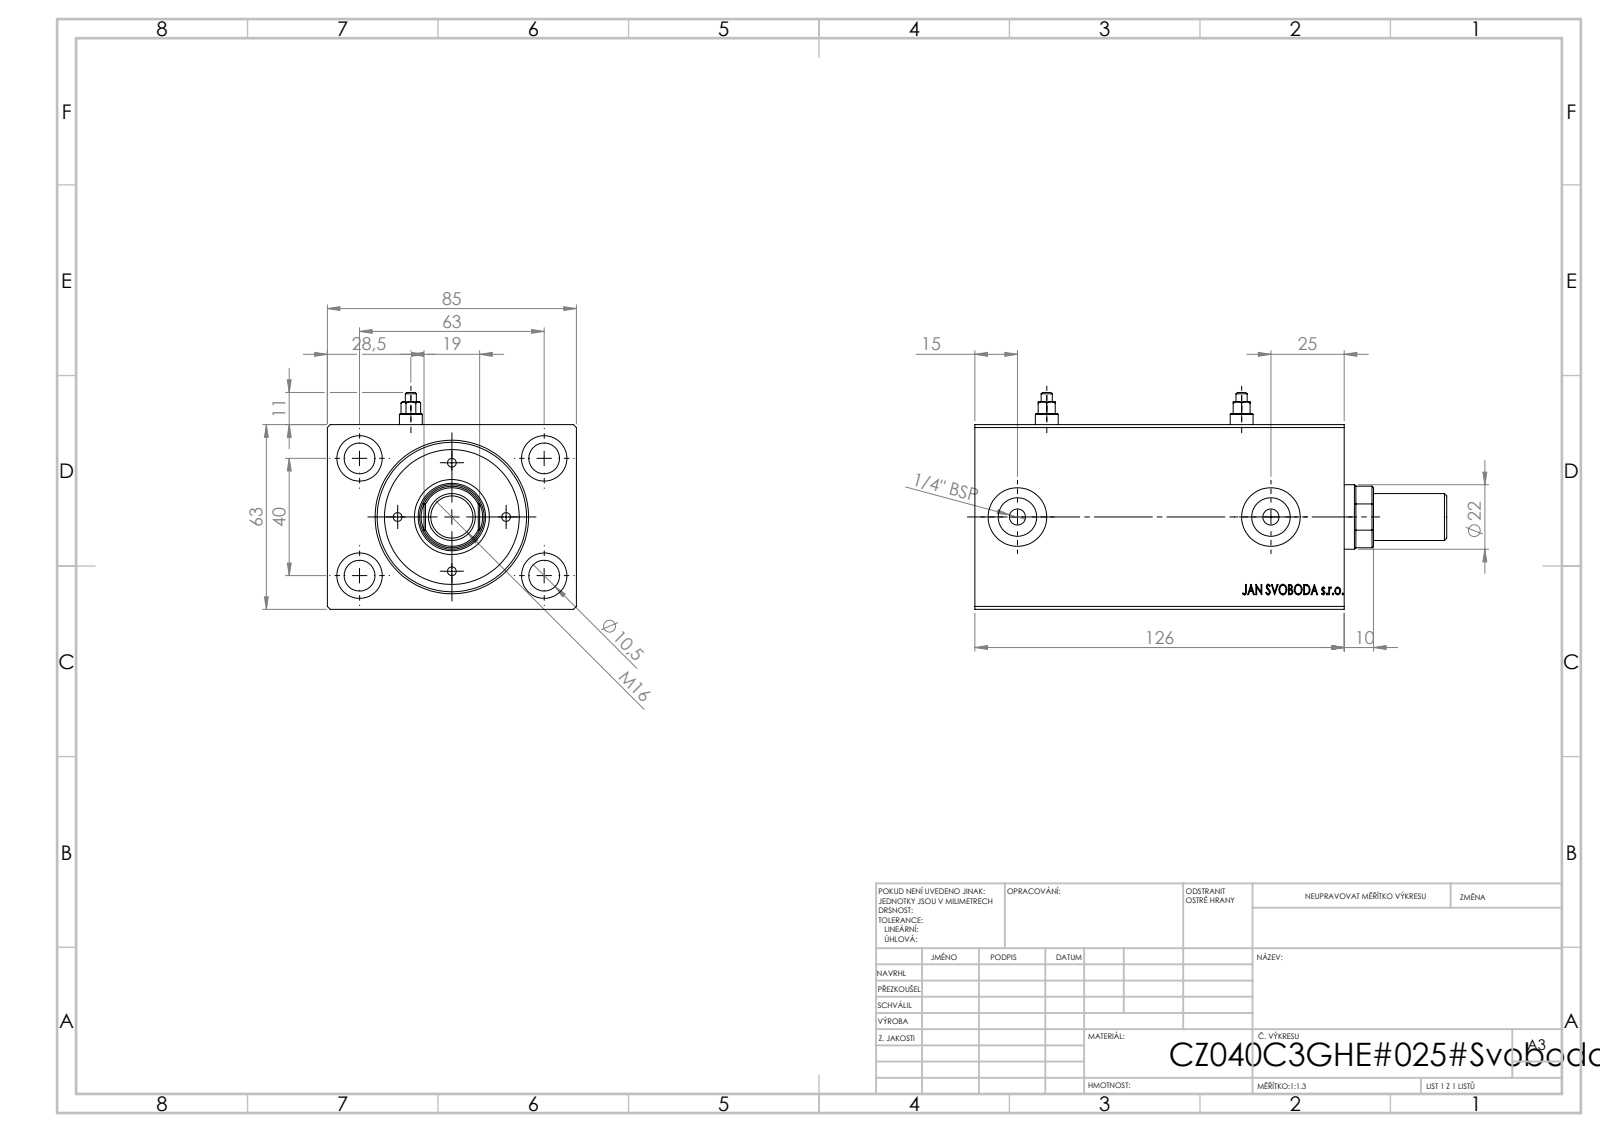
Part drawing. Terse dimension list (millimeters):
written by: SolidWorks 2019 (CONFIG_CONTROL_DESIGN)
unit: mm
bodies: 1 solid, 825 faces (397 planar, 46 cylindrical, 382 other)
size: 126 × 85 × 63
volume: 471 004 mm³; area: 80 723 mm²
holes: 4× ⌀10.5, 4× ⌀15.5, 2× ⌀5.5, 2× ⌀8, 2× ⌀13.16, 2× ⌀20, 1× ⌀36, 1× ⌀40, 1× ⌀51
face distances: 63, 85, 126, 110.7, 15.3, 125.8, 15.1, 10.33, 115.67, 10
hole spacings: 37.31, 40, 63, 74.63, 66.5, 86.5
